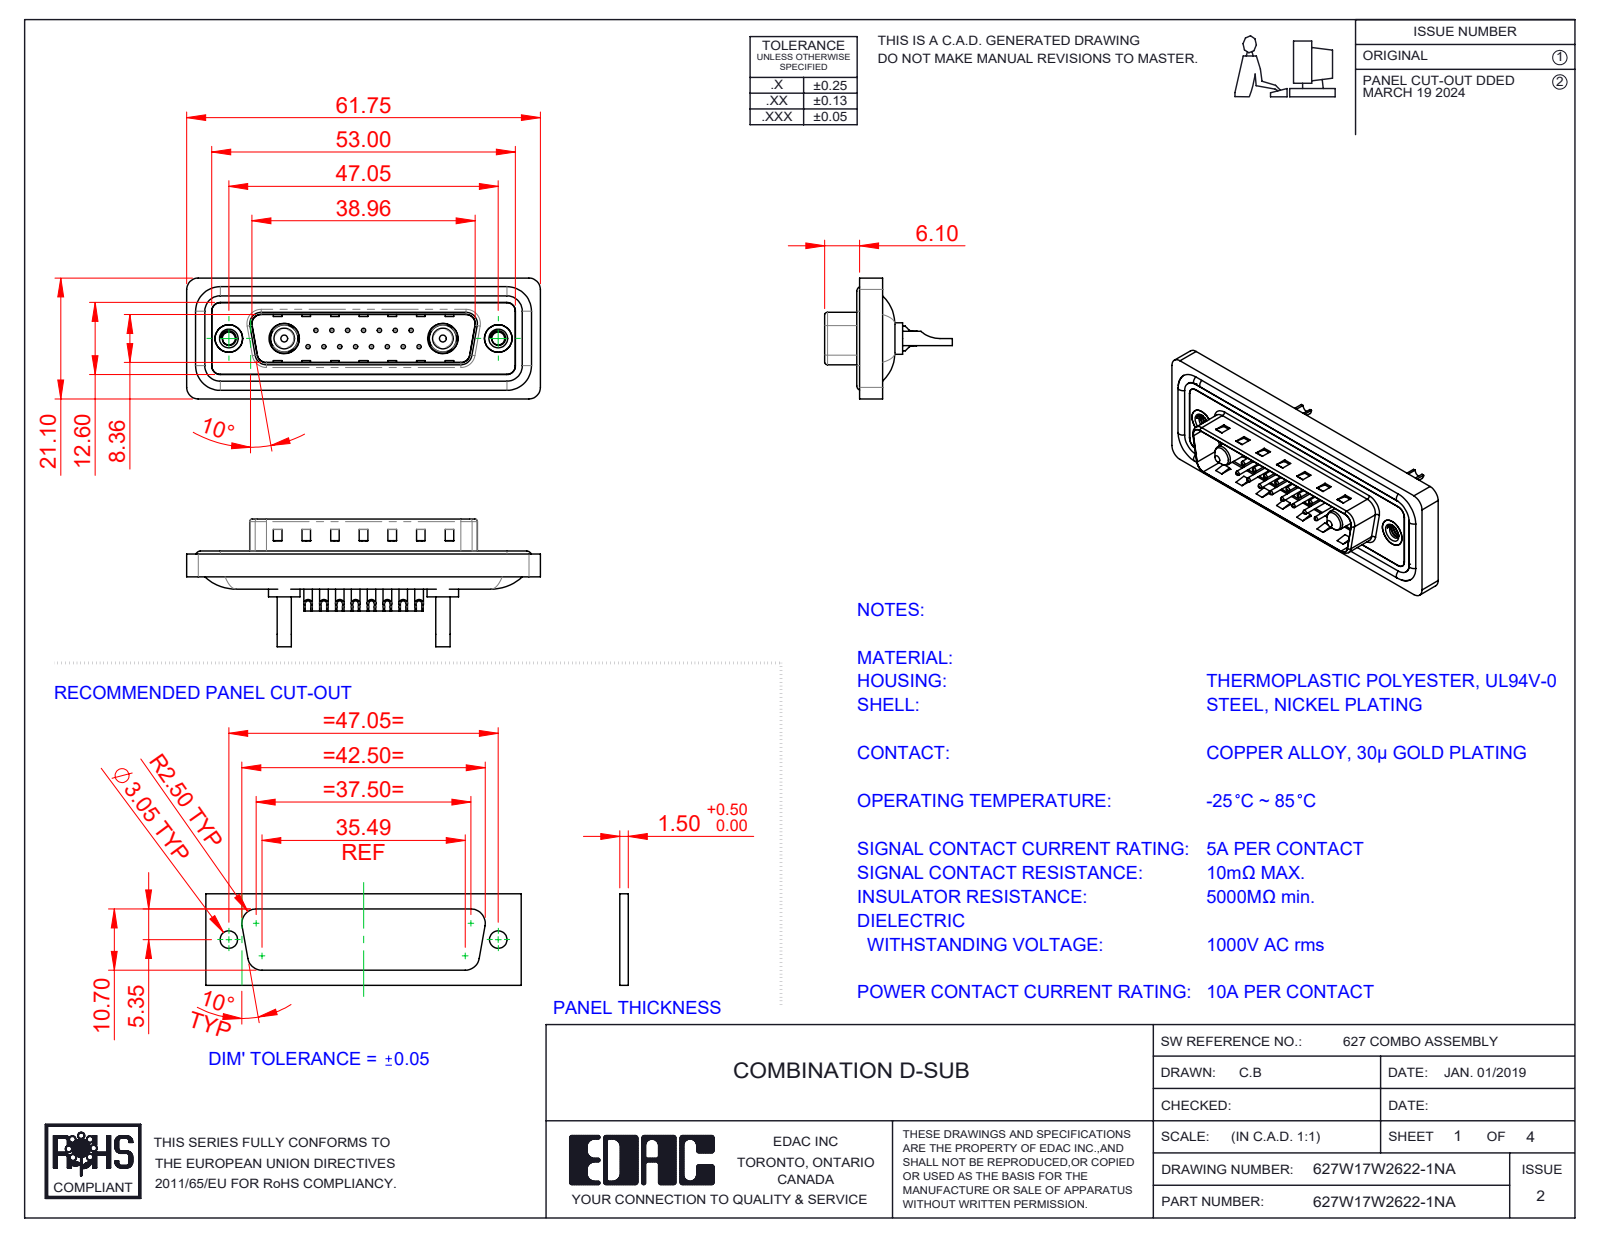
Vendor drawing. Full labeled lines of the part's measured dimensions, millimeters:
Part name (STEP PRODUCT): 627Combo Waterproof Housing_25 Contacts; 627Combo Contact Row 1_22; 627Combo Housing_17W2; 627W17W2622-1NA (+5 more)
STEP written by: SolidWorks 2023 (CONFIG_CONTROL_DESIGN)
Units: millimetres
Bodies: 26 solids, 1126 faces (368 planar, 474 cylindrical, 284 other)
Overall size (bounding box): 61.75 × 22.3 × 21.1
Volume: 7 286 mm³ · Surface area: 12 126 mm²
Round holes (diameter × count): ⌀0.75 ×15, ⌀1 ×15, ⌀1.6 ×15, ⌀2 ×15, ⌀1.7 ×2, ⌀2.26 ×2, ⌀4 ×2, ⌀4.8 ×2, ⌀4.85 ×2, ⌀5 ×2, ⌀5.3 ×2
Round bosses / shafts (diameter × count): ⌀1.5 ×15, ⌀1.6 ×4, ⌀5.5 ×2, ⌀5.2 ×2, ⌀4.9 ×2, ⌀4.75 ×2, ⌀3.75 ×2, ⌀3.6 ×2
Partial cylindrical surfaces — rounded edges, fillets, slot ends (radius × count): R1.5 ×22, R2 ×18, R0.5 ×8, R1.6 ×8, R1 ×6, R0.25 ×4, R0.6 ×4, R0.65 ×4
Main face-to-face distances: 0.4, 1.5, 1.1, 1.6, 0.5, 3.1, 2.9, 0.82, 9.58, 4.1
Hole centre spacings: 3.16, 2.77, 5.54, 8.31, 5.04, 7.49, 11.08, 5.03
